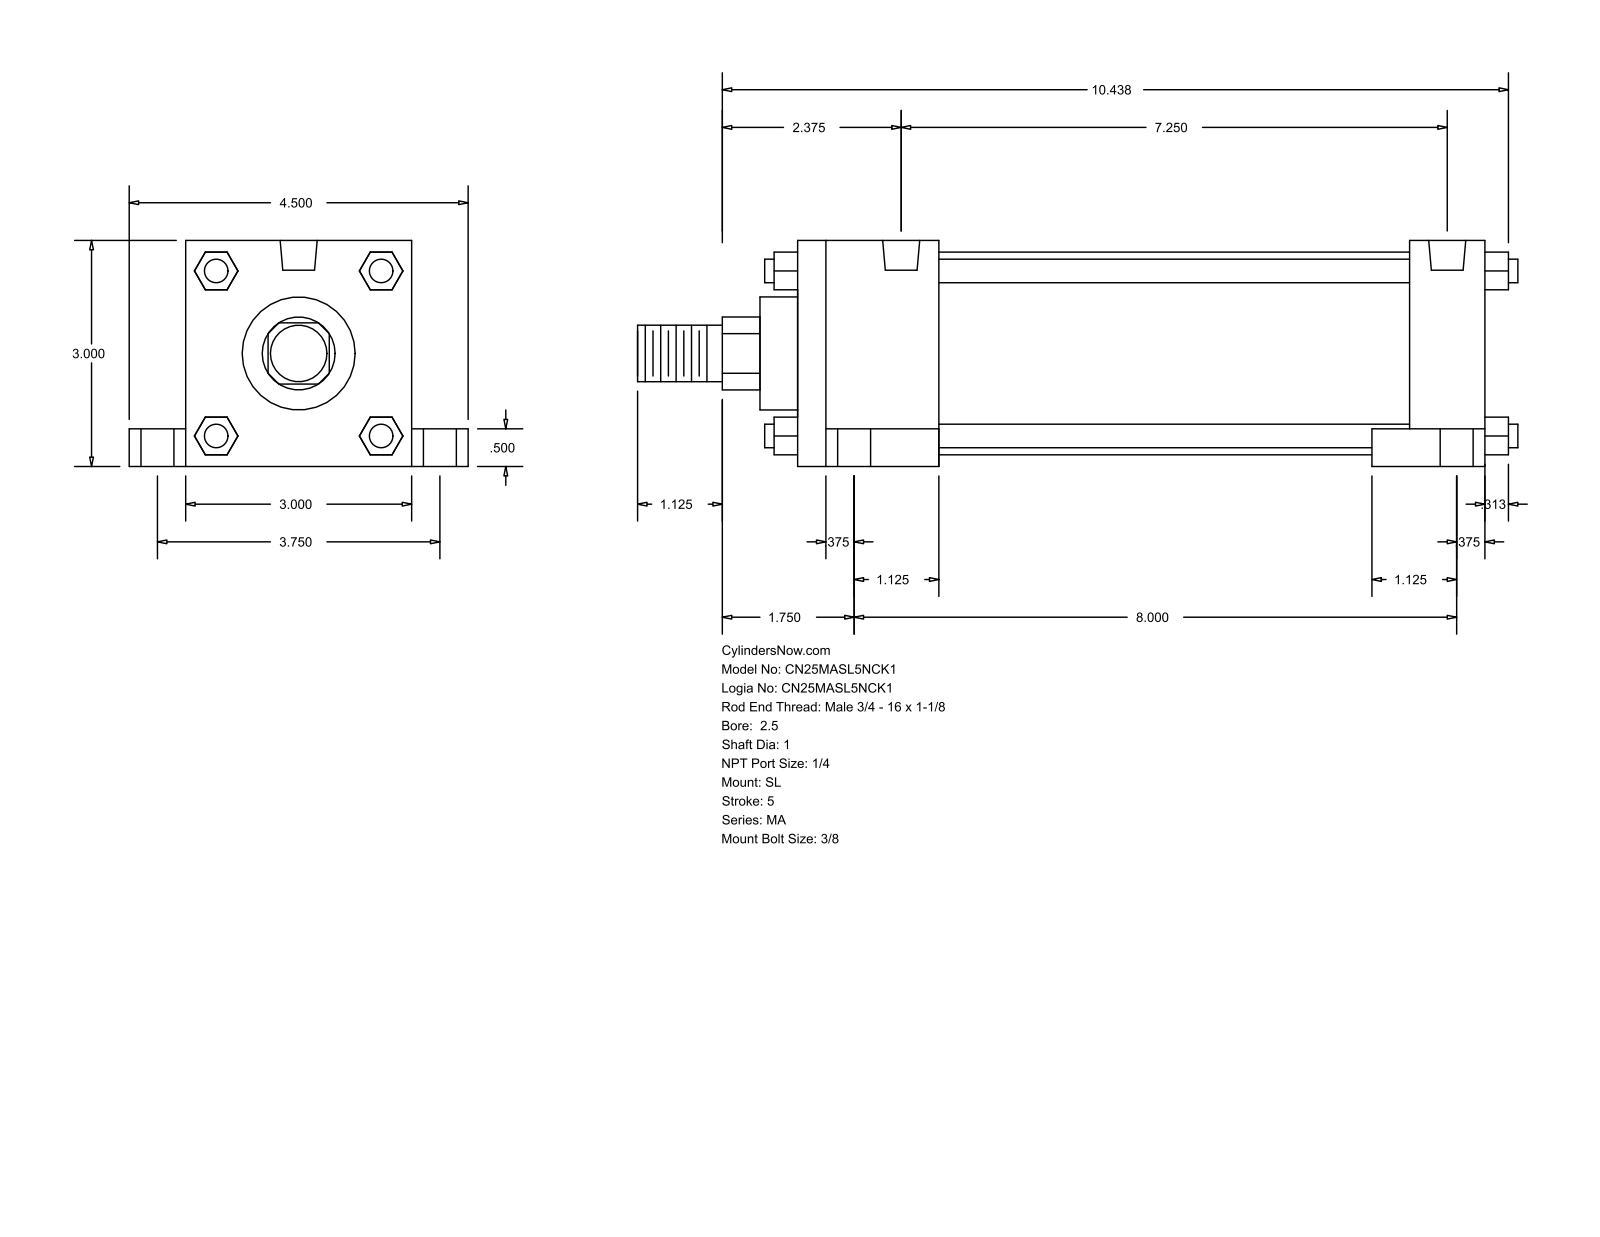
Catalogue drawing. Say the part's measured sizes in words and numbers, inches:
The part is named "MA_SL__0250_1". Its 3-D file was written by "GSSL Pune (CONFIG_CONTROL_DESIGN)". It is 0 solids with 148 faces: 112 planar, 36 cylindrical and 0 other. Overall it measures 11.687 by 4.5 by 3 inches. Round holes: 4 of diameter 0.313, 4 of diameter 0.437, 4 of diameter 0.687, 2 of diameter 0.492. Round bosses or shafts: 4 of diameter 0.313, 1 of diameter 2.69, 1 of diameter 1.5, 1 of diameter 1, 1 of diameter 0.75. Partial cylindrical surfaces (rounded edges, fillets, slot ends): 1 of radius 0.484. The main face-to-face distances are 3, 9.125, 0.5, 6.25, 1, 1.875, 7.25, 8.125, 0.75, 3.75. The hole center spacings are 1.879, 1.976, 3.75, 7.25, 7.609, 8, 8.095, 8.835.
